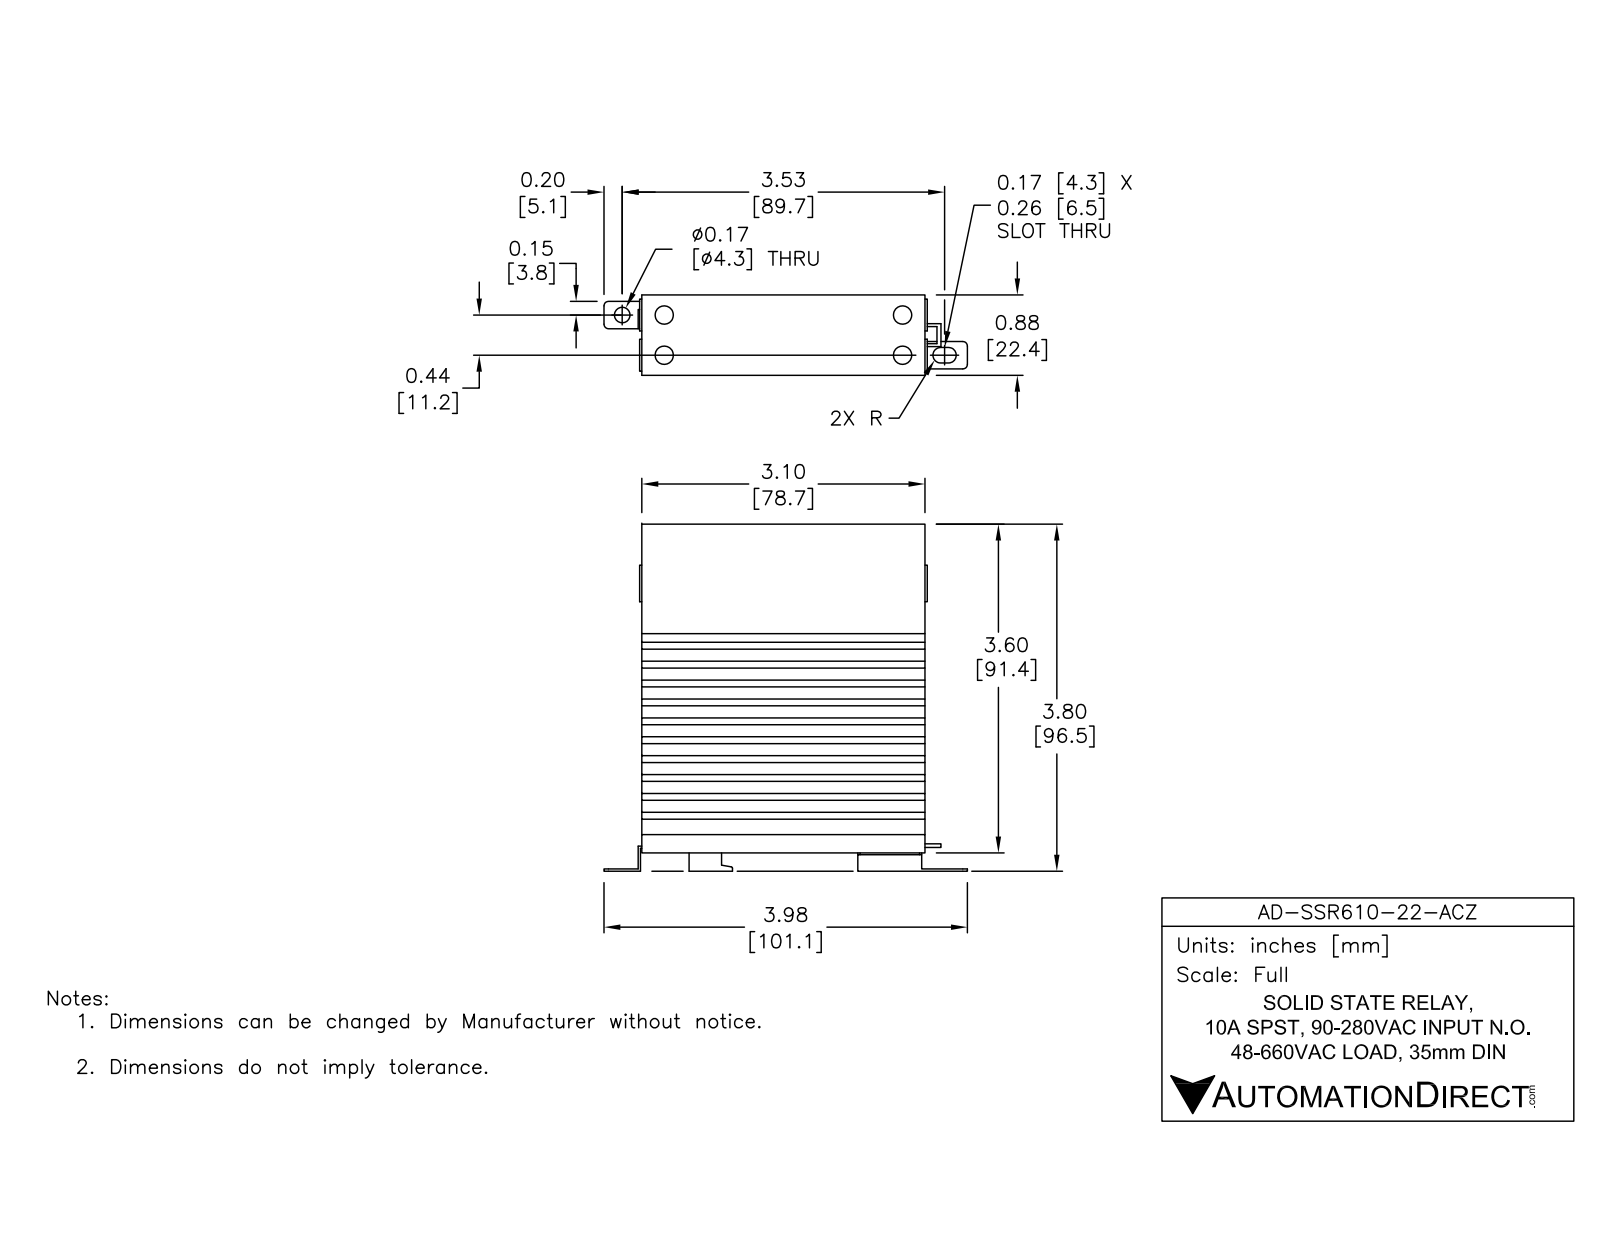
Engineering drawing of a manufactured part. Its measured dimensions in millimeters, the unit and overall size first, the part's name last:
Units: millimetres
Overall size (bounding box): 101.1 × 96.5 × 22.4
Round holes (diameter × count): ⌀5.1 ×4, ⌀4.3 ×1
Partial cylindrical surfaces — rounded edges, fillets, slot ends (radius × count): R1.3 ×6, R2.2 ×2, R0.4 ×1
Main face-to-face distances: 15.7, 5.3, 21, 10.5, 3.4, 12.4, 8.6, 10.5, 1.9, 5.3
Hole centre spacings: 11.2, 66.3, 67.2, 11.7, 16.2, 78, 78.8
Volume: 116 900 mm³ · Surface area: 48 330 mm²
Bodies: 1 solid, 215 faces (195 planar, 20 cylindrical, 0 other)
Part name (STEP PRODUCT): AD-SSR610-22-ACZ
STEP written by: SolidWorks 2014 (AUTOMOTIVE_DESIGN)
